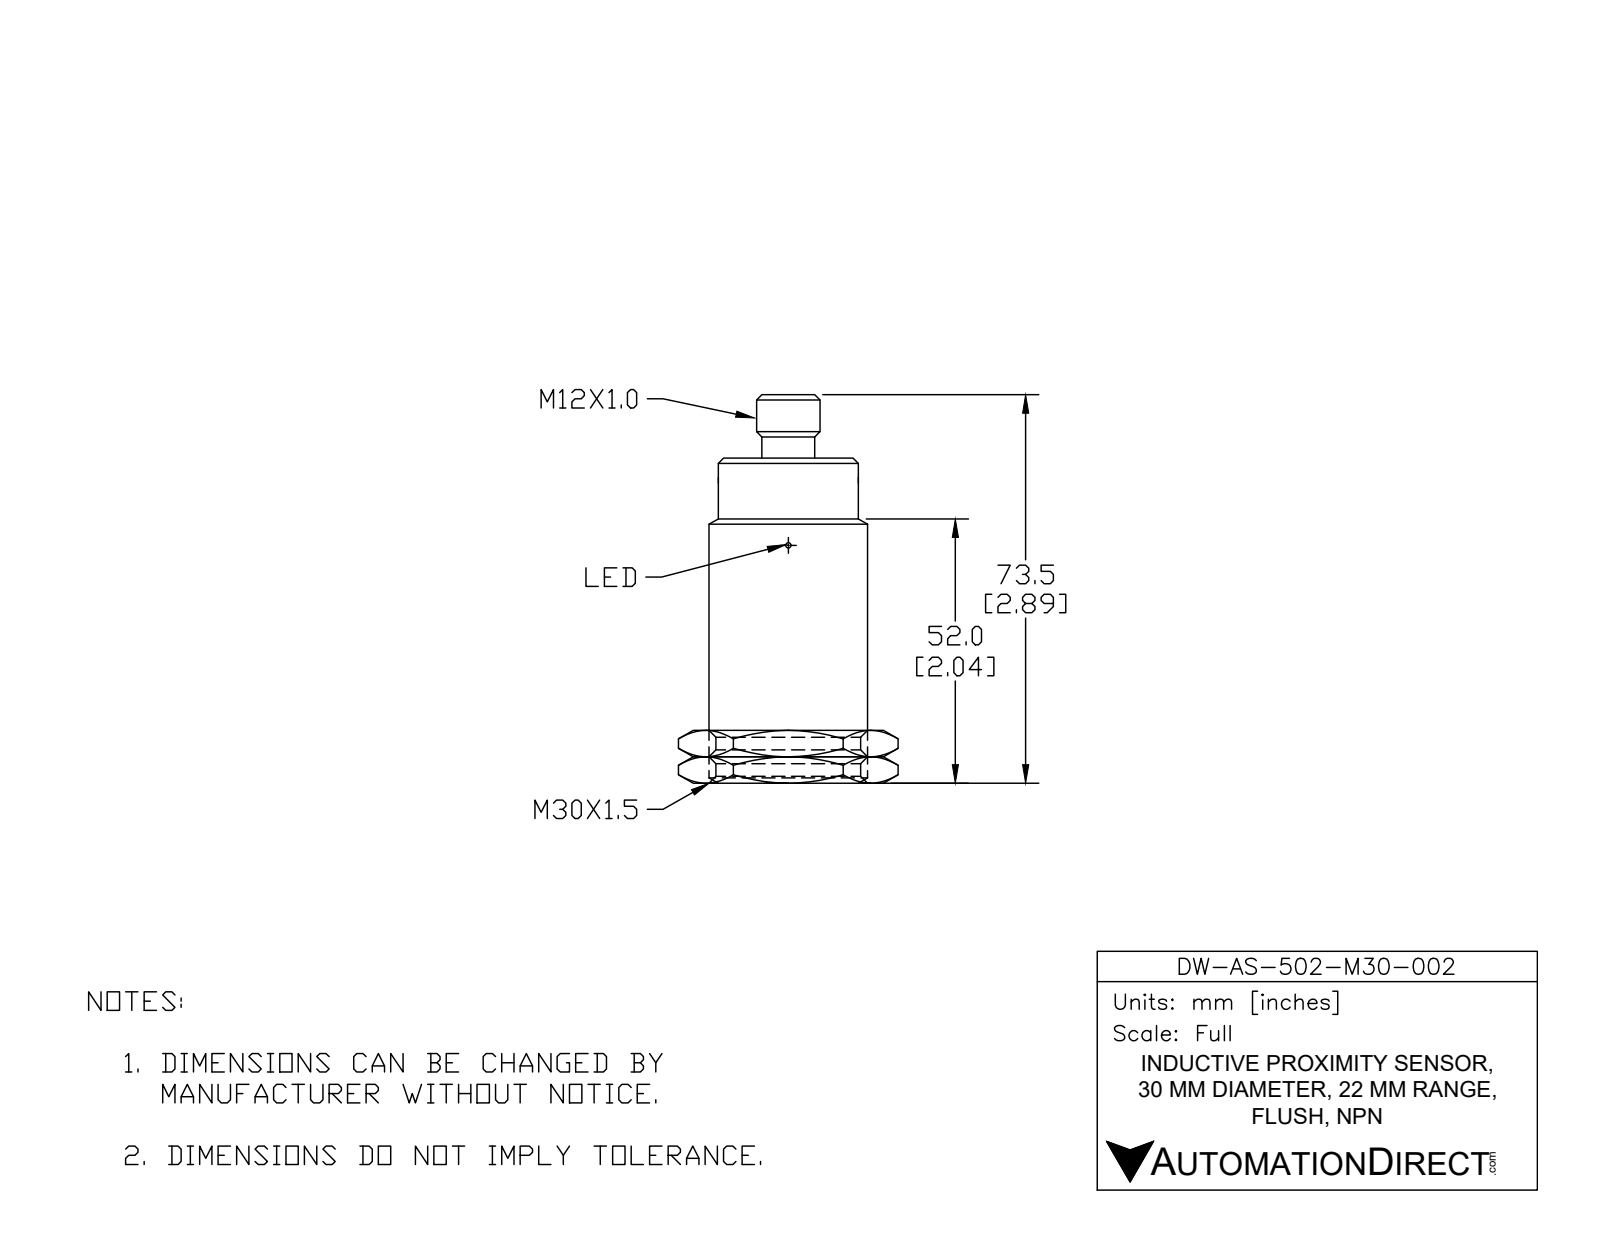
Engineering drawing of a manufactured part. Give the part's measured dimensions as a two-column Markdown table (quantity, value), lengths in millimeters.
| quantity | value |
| --- | --- |
| part name | DW-AS-512-M30-002 |
| STEP written by | SolidWorks 2017 (AUTOMOTIVE_DESIGN) |
| units | millimeters |
| bodies | 1 solid, 38 faces (8 planar, 20 cylindrical, 10 other) |
| overall size | 73.5 × 30 × 30 |
| volume | 42 610 mm³ |
| surface area | 7 813 mm² |
| round holes (diameter × count) | 3 × 2, 8.5 × 1 |
| round bosses / shafts (diameter × count) | 1 × 4, 30 × 1, 27.5 × 1, 12 × 1, 10.5 × 1 |
| partial cylindrical surfaces (radius × count) | 0.6 × 2, 4.9 × 1 |
| main face-to-face distances | 60.5, 64.8, 4.4, 52.1, 8.4, 12.8, 73.5, 21.5, 13.1, 8.7 |
